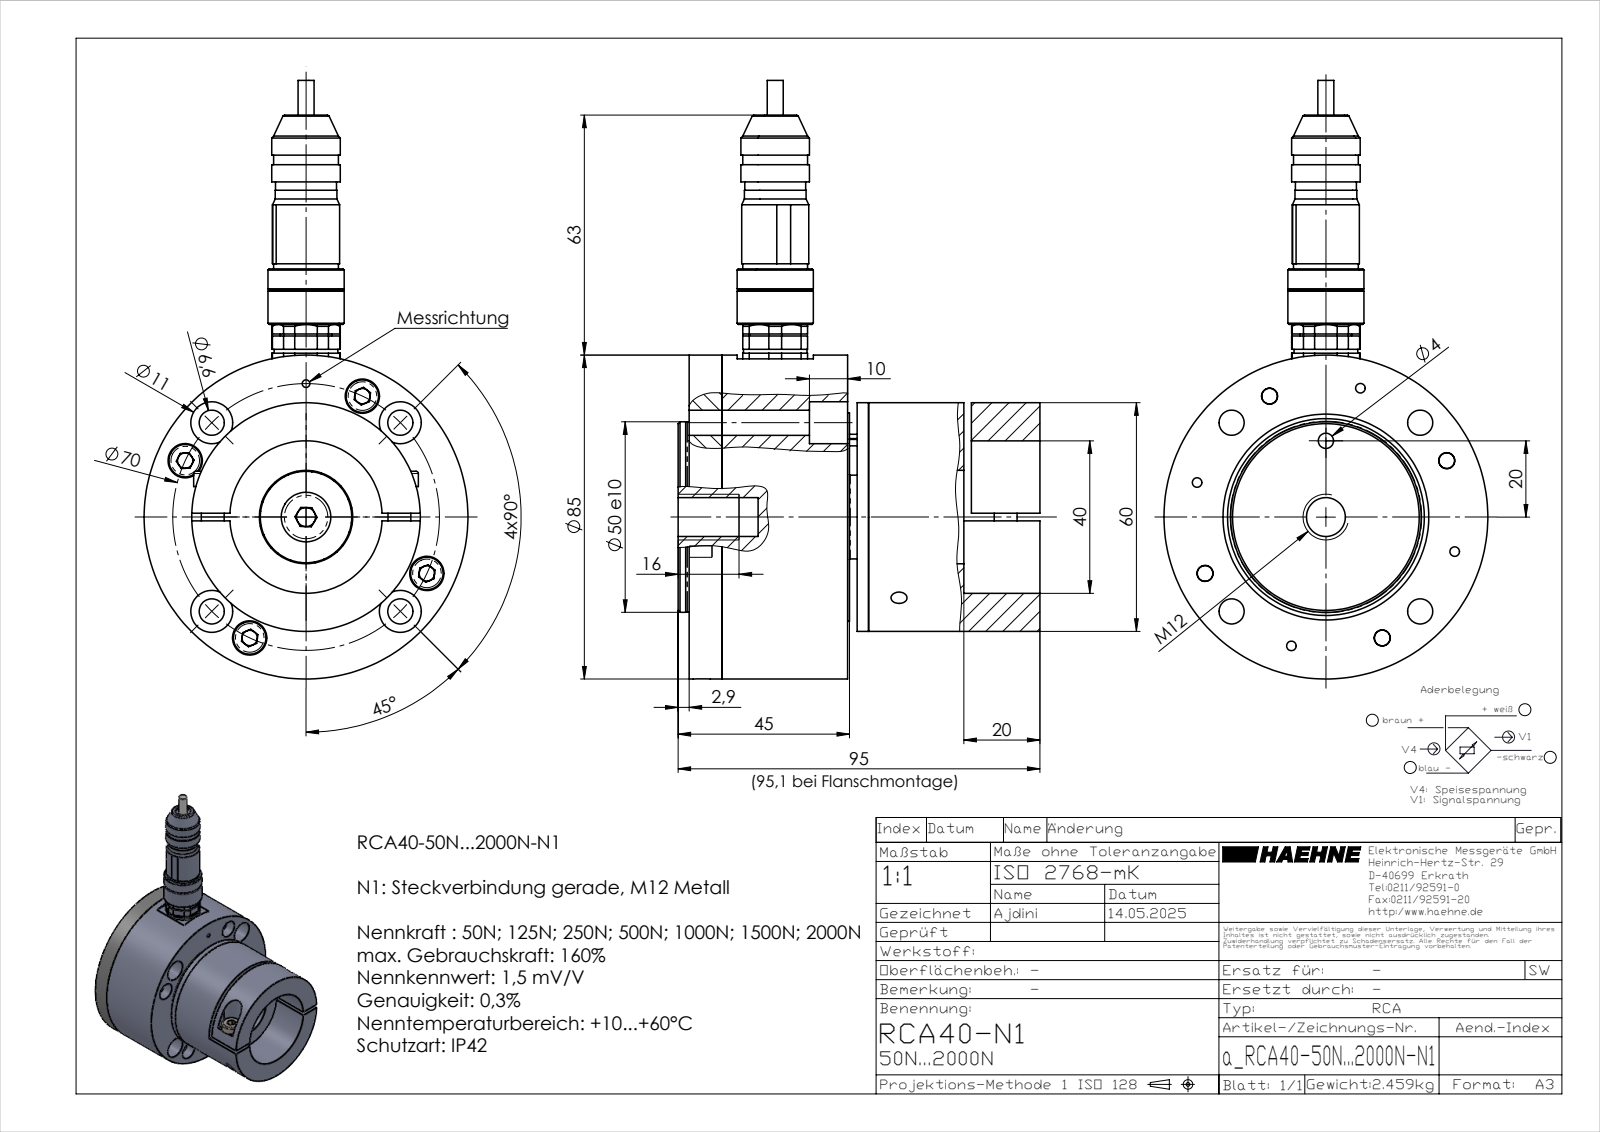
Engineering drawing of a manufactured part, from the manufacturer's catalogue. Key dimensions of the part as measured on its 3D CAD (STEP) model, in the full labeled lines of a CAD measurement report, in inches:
Part name (STEP PRODUCT): inafag_1203-tvh_7zkvytp7yxkimpdvw8sj0b5w4_22; inafag_1203-tvh_7zkvytp7yxkimpdvw8sj0b5w4_12; a_RCA40-50N...2000N-N1; inafag_1203-tvh_7zkvytp7yxkimpdvw8sj0b5w4_01 (+8 more)
STEP written by: SolidWorks 2023 (AUTOMOTIVE_DESIGN)
Units: inches
Bodies: 54 solids, 743 faces (377 planar, 203 cylindrical, 163 other)
Overall size (bounding box): 6.183 × 3.744 × 3.346
Volume: 21.94 in³ · Surface area: 176.3 in²
Round holes (diameter × count): ⌀0.134 ×9, ⌀0.098 ×8, ⌀0.26 ×6, ⌀0.039 ×5, ⌀0.165 ×5, ⌀0.157 ×4, ⌀0.209 ×4, ⌀0.354 ×4, ⌀0.433 ×4, ⌀0.177 ×2, ⌀0.197 ×2, ⌀0.079 ×1
Round bosses / shafts (diameter × count): ⌀0.118 ×9, ⌀0.224 ×8, ⌀0.335 ×4, ⌀0.197 ×4, ⌀0.059 ×4, ⌀0.039 ×4, ⌀0.669 ×2, ⌀0.394 ×2
Partial cylindrical surfaces — rounded edges, fillets, slot ends (radius × count): R0.012 ×6, R0.039 ×4, R0.217 ×2, R0.022 ×1, R0.024 ×1, R0.03 ×1, R0.138 ×1
Main face-to-face distances: 0.118, 0.339, 1.854, 0.079, 0.457, 1.181, 1.398, 1.516, 1.972, 1.772
Hole centre spacings: 1.378, 1.949, 0.976, 0.992, 1.291, 2.013, 2.223, 0.098
